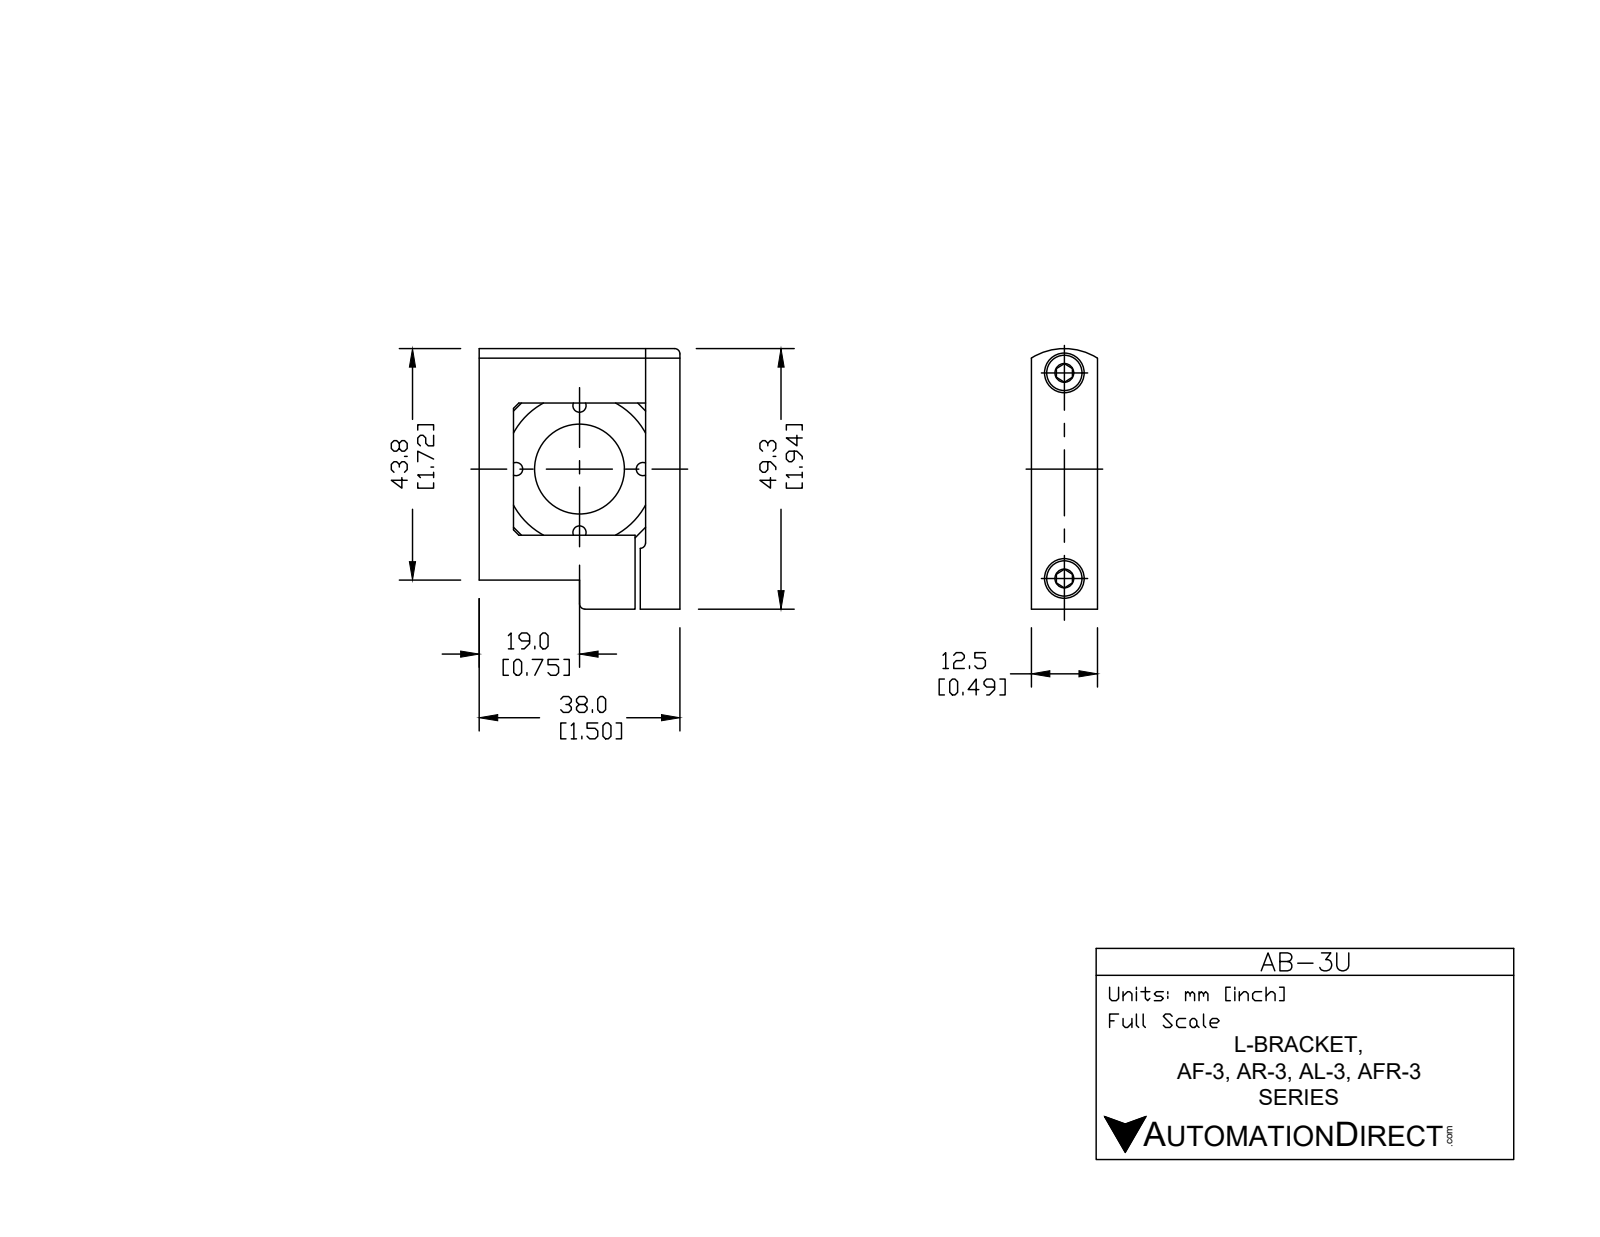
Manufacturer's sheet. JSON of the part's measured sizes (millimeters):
{"part_name": "AB-3U", "step_written_by": "SolidWorks 2015 (CONFIG_CONTROL_DESIGN)", "units": "millimeters", "bodies": {"solids": 3, "faces": 92, "planar": 60, "cylindrical": 20, "other": 12}, "overall_size": [49.3, 38, 12.5], "volume_mm3": 13538, "surface_area_mm2": 8324, "round_holes": [[4.5, 2], [6.21, 2], [17, 1]], "round_bosses_or_shafts": [[5.75, 2], [4, 2]], "partial_cylinders_radius": [[1.5, 1], [11.75, 1]], "face_to_face_distances": [12.5, 2, 6.5, 38, 33.5, 4.5, 27, 29, 10.5, 5.81], "hole_center_spacings": [38.9]}
